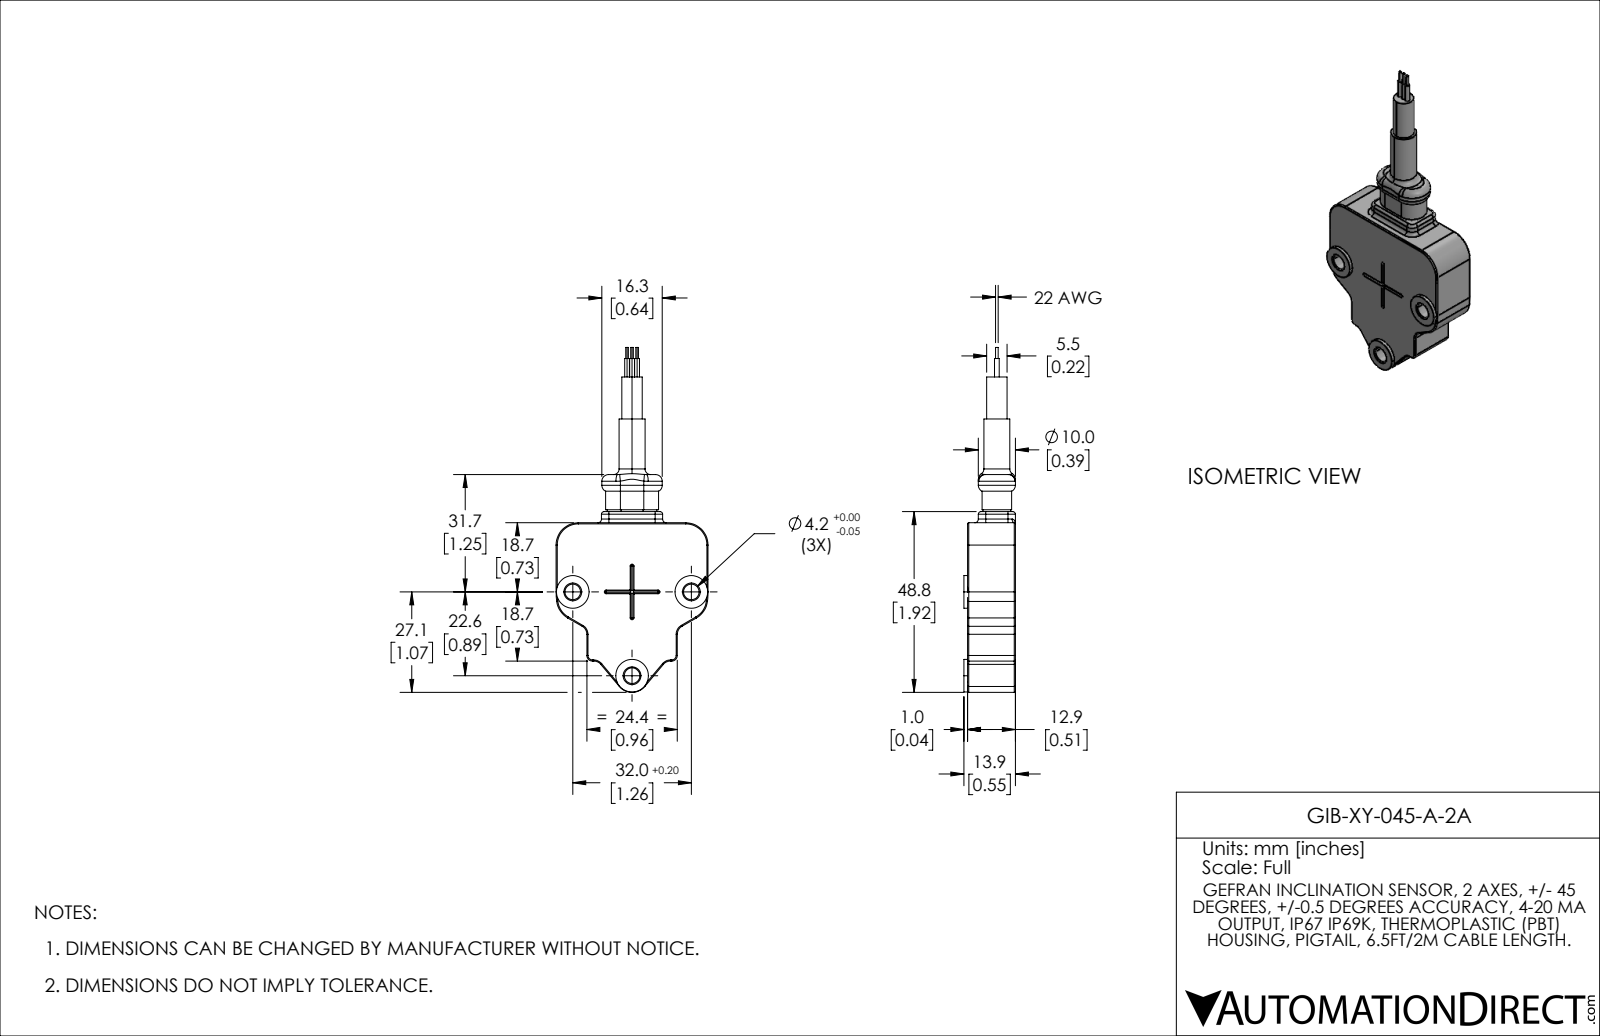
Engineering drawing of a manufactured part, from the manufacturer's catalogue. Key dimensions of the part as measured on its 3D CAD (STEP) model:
Part name (STEP PRODUCT): GIB-XY-045-A-2A
STEP written by: SolidWorks 2021 (AUTOMOTIVE_DESIGN)
Units: inches
Bodies: 1 solid, 201 faces (47 planar, 87 cylindrical, 67 other)
Overall size (bounding box): 3.663 × 1.614 × 0.547
Volume: 1.246 in³ · Surface area: 9.975 in²
Round holes (diameter × count): ⌀0.165 ×3
Round bosses / shafts (diameter × count): ⌀0.346 ×3, ⌀0.051 ×3, ⌀0.028 ×3, ⌀0.276 ×1, ⌀0.217 ×1
Partial cylindrical surfaces — rounded edges, fillets, slot ends (radius × count): R0.012 ×20, R0.008 ×4, R0.028 ×4, R0.079 ×4, R0.098 ×4, R0.236 ×4, R0.039 ×3, R0.059 ×2
Main face-to-face distances: 0.508, 0.039, 1.614, 0.327, 1.287, 0.547, 0.961, 0.354, 0.154, 0.118
Hole centre spacings: 1.09, 1.26
